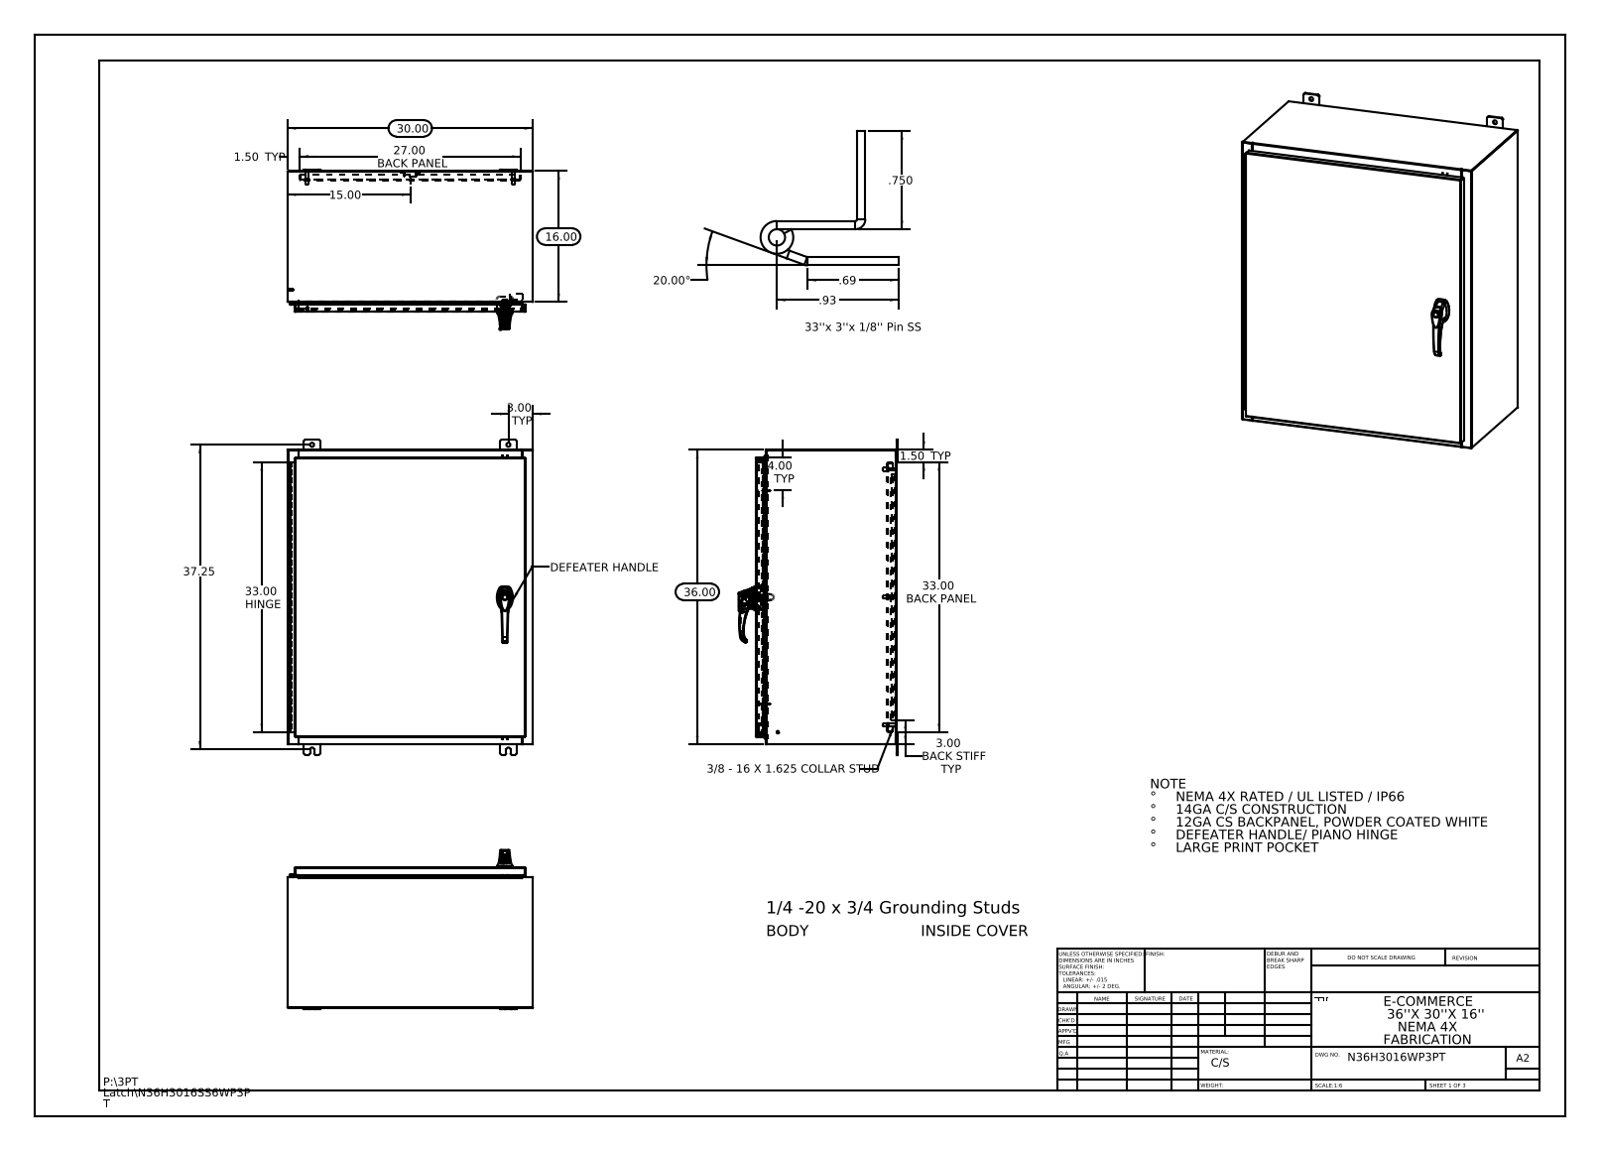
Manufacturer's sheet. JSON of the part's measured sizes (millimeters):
{"part_name": "N36H3016SS6WP3PT Enclosure Stiffener; N36H3016SS6WP3PT Hinge Enclosure Side2; g26103103_26163303; N36H3016SS6WP3PT Defeater Handle Rod (+8 more)", "step_written_by": "SolidWorks 2013 (CONFIG_CONTROL_DESIGN)", "units": "millimeters", "bodies": {"solids": 40, "faces": 2894, "planar": 1083, "cylindrical": 1093, "other": 718}, "overall_size": [977.9, 762, 495.2], "volume_mm3": 7668000, "surface_area_mm2": 7555000, "round_holes": [[12.7, 10], [6.4, 4], [3.5, 3], [4.1, 3], [2, 2], [5.2, 2], [8, 2], [11.1, 2], [3.2, 1], [3.2, 1], [5, 1], [7, 1]], "round_bosses_or_shafts": [[15.9, 6], [9.5, 6], [8.4, 6], [4, 4], [3.6, 4], [8, 3], [6, 3], [30, 1]], "partial_cylinders_radius": [[3, 37], [0.2, 33], [0.3, 28], [4.8, 24], [2.2, 22], [1, 15], [0.7, 12], [0.2, 6]], "face_to_face_distances": [1.9, 435, 760.1, 433.1, 2.6, 436.9, 912.5, 25.4, 409.6, 27.3], "hole_center_spacings": [288.6, 347.2, 396.9, 754.2, 641.4, 714.5, 7.5, 15.9]}
